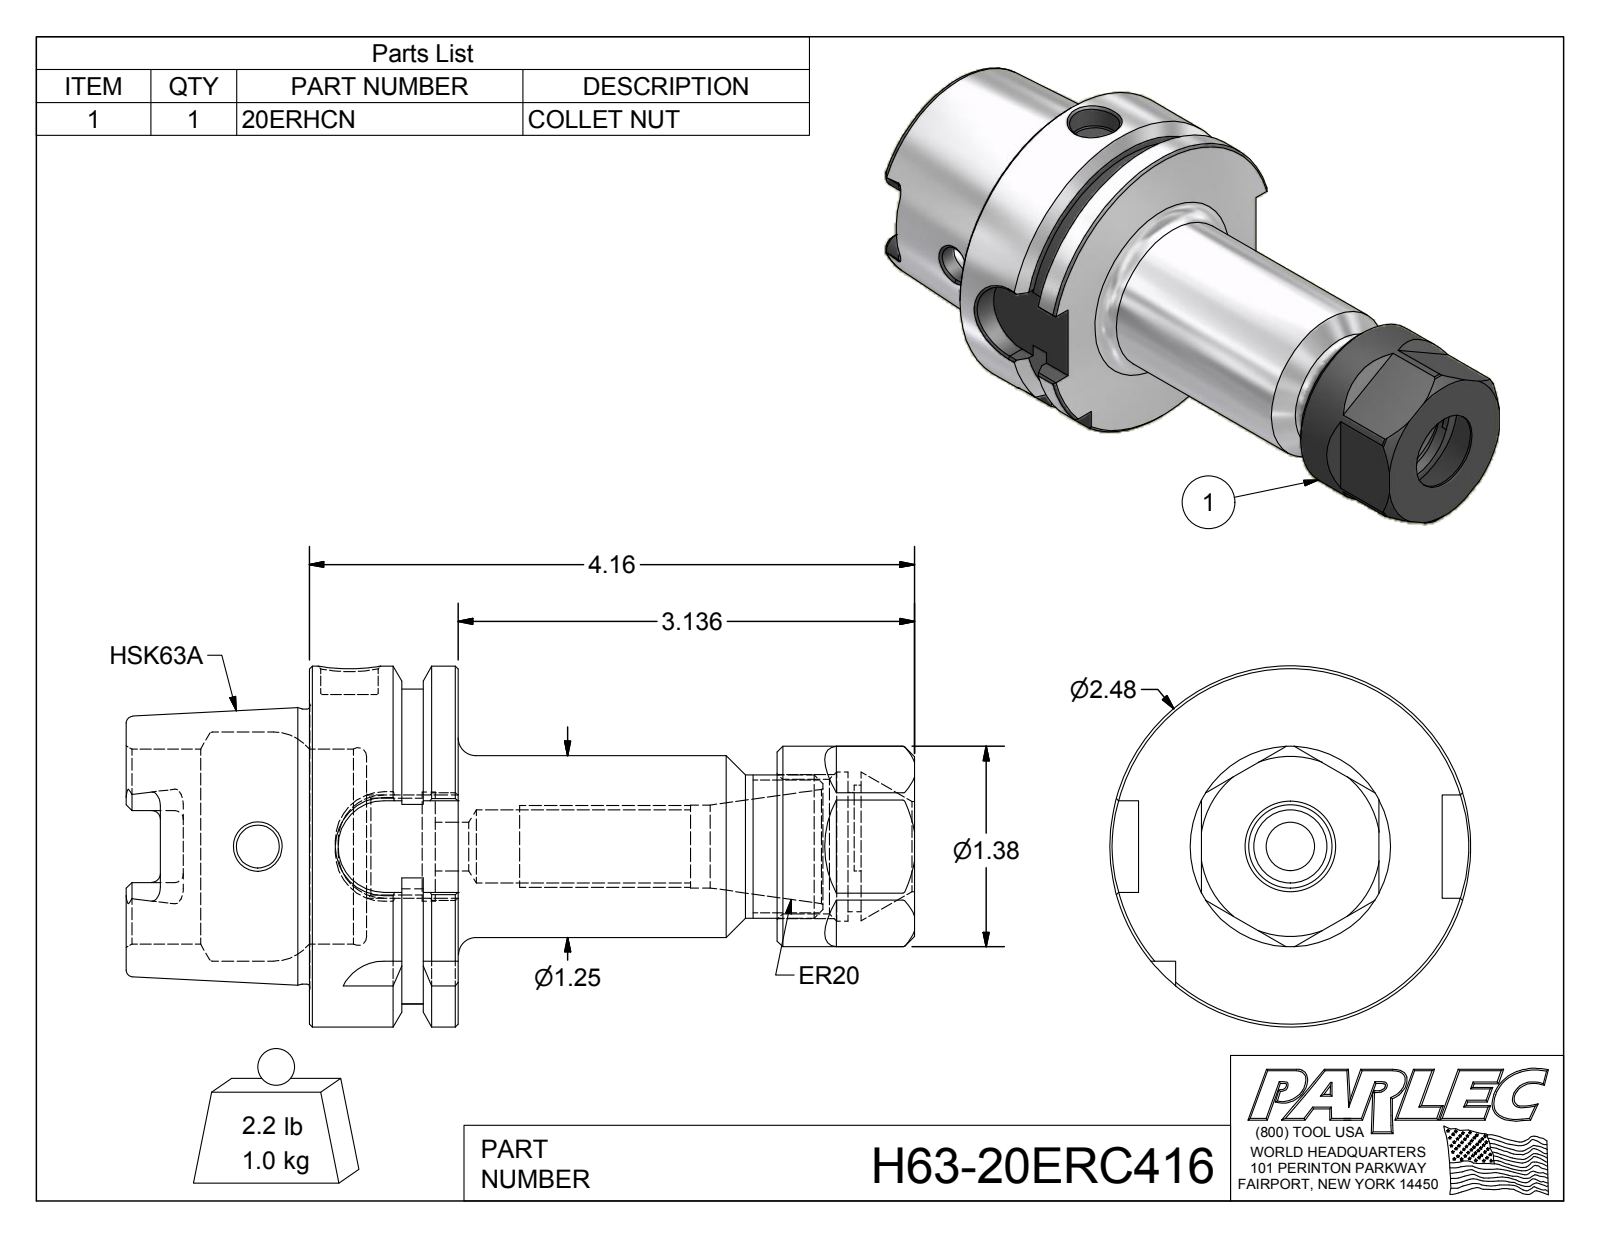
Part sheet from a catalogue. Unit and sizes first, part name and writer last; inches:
Units: inches
Overall size (bounding box): 5.42 × 2.48 × 2.48
Round holes (diameter × count): ⌀0.295 ×1, ⌀0.335 ×1, ⌀0.394 ×1, ⌀0.502 ×1, ⌀0.57 ×1, ⌀0.62 ×1, ⌀0.666 ×1, ⌀0.749 ×1, ⌀0.82 ×1, ⌀0.925 ×1, ⌀1.024 ×1, ⌀1.339 ×1
Round bosses / shafts (diameter × count): ⌀2.48 ×1, ⌀1.891 ×1, ⌀1.378 ×1, ⌀1.25 ×1, ⌀0.984 ×1
Partial cylindrical surfaces — rounded edges, fillets, slot ends (radius × count): R0.059 ×6, R0.113 ×4, R0.315 ×4, R0.423 ×1, R1.083 ×1
Main face-to-face distances: 1.024, 1.654, 0.241, 0.389, 1.22, 3.136, 0.63, 0.394, 4.16, 3.766
Hole centre spacings: 0.037
Volume: 7.824 in³ · Surface area: 56.81 in²
Bodies: 2 solids, 177 faces (69 planar, 42 cylindrical, 66 other)
Part name (STEP PRODUCT): H63-20ERC416; H63-20ER4-1; 20ERHCN
STEP written by: Autodesk Inventor 2012 (AUTOMOTIVE_DESIGN)
